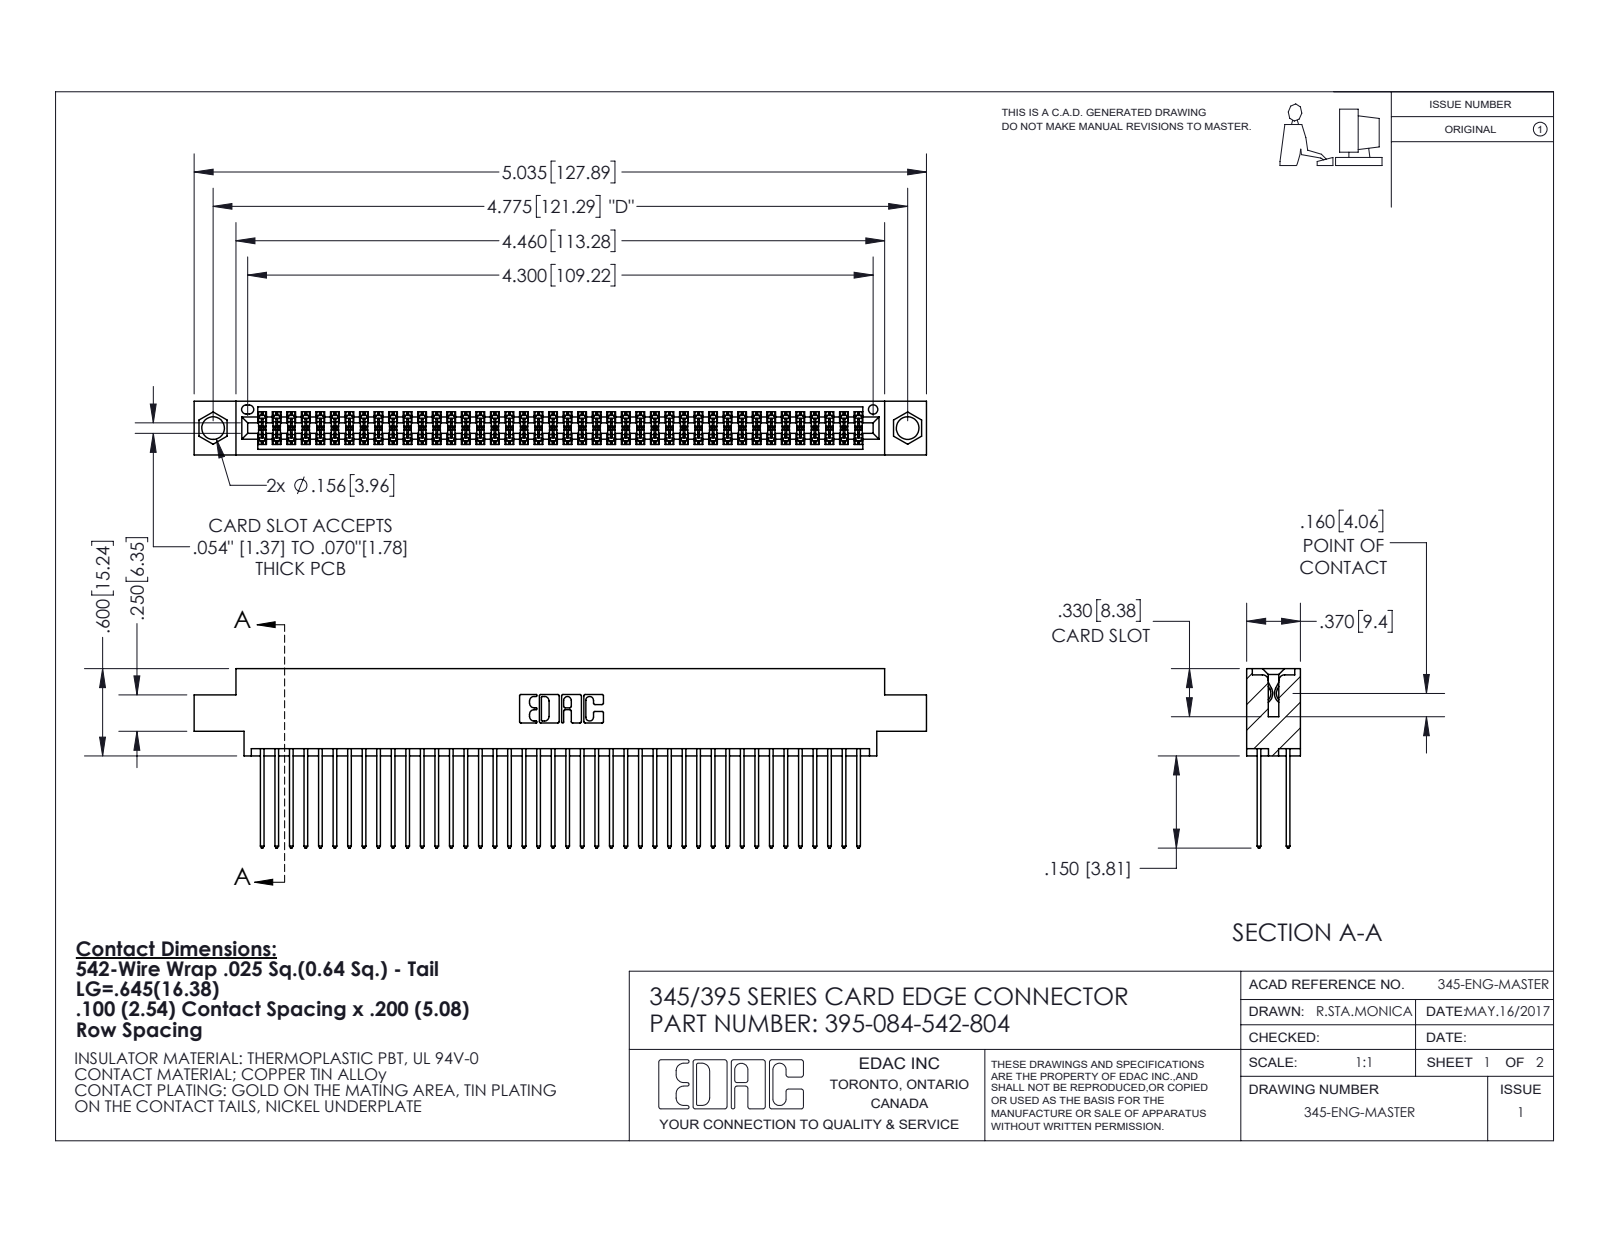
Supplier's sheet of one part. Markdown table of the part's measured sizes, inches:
| quantity | value |
| --- | --- |
| part name | 345-292-001_345-293-142; 395-084-542-804; 345 Part_0.170 Offset - 0.156 Dia-TI |
| STEP written by | SolidWorks 2020 (CONFIG_CONTROL_DESIGN) |
| units | inches |
| bodies | 85 solids, 4344 faces (2870 planar, 1474 cylindrical, 0 other) |
| overall size | 5.035 × 1.232 × 0.37 |
| volume | 0.769 in³ |
| surface area | 31.69 in² |
| round holes (diameter × count) | 0.156 × 2, 0.064 × 1 |
| partial cylindrical surfaces (radius × count) | 0.006 × 126, 0.01 × 84, 0.01 × 22, 0.007 × 6, 0.031 × 6, 0.026 × 3, 0.014 × 2, 0.019 × 2 |
| main face-to-face distances | 0.072, 0.298, 0.2, 0.098, 0.272, 0.025, 0.37, 0.225, 0.175, 0.149 |
| hole center spacings | 0.27, 4.539, 4.775 |
